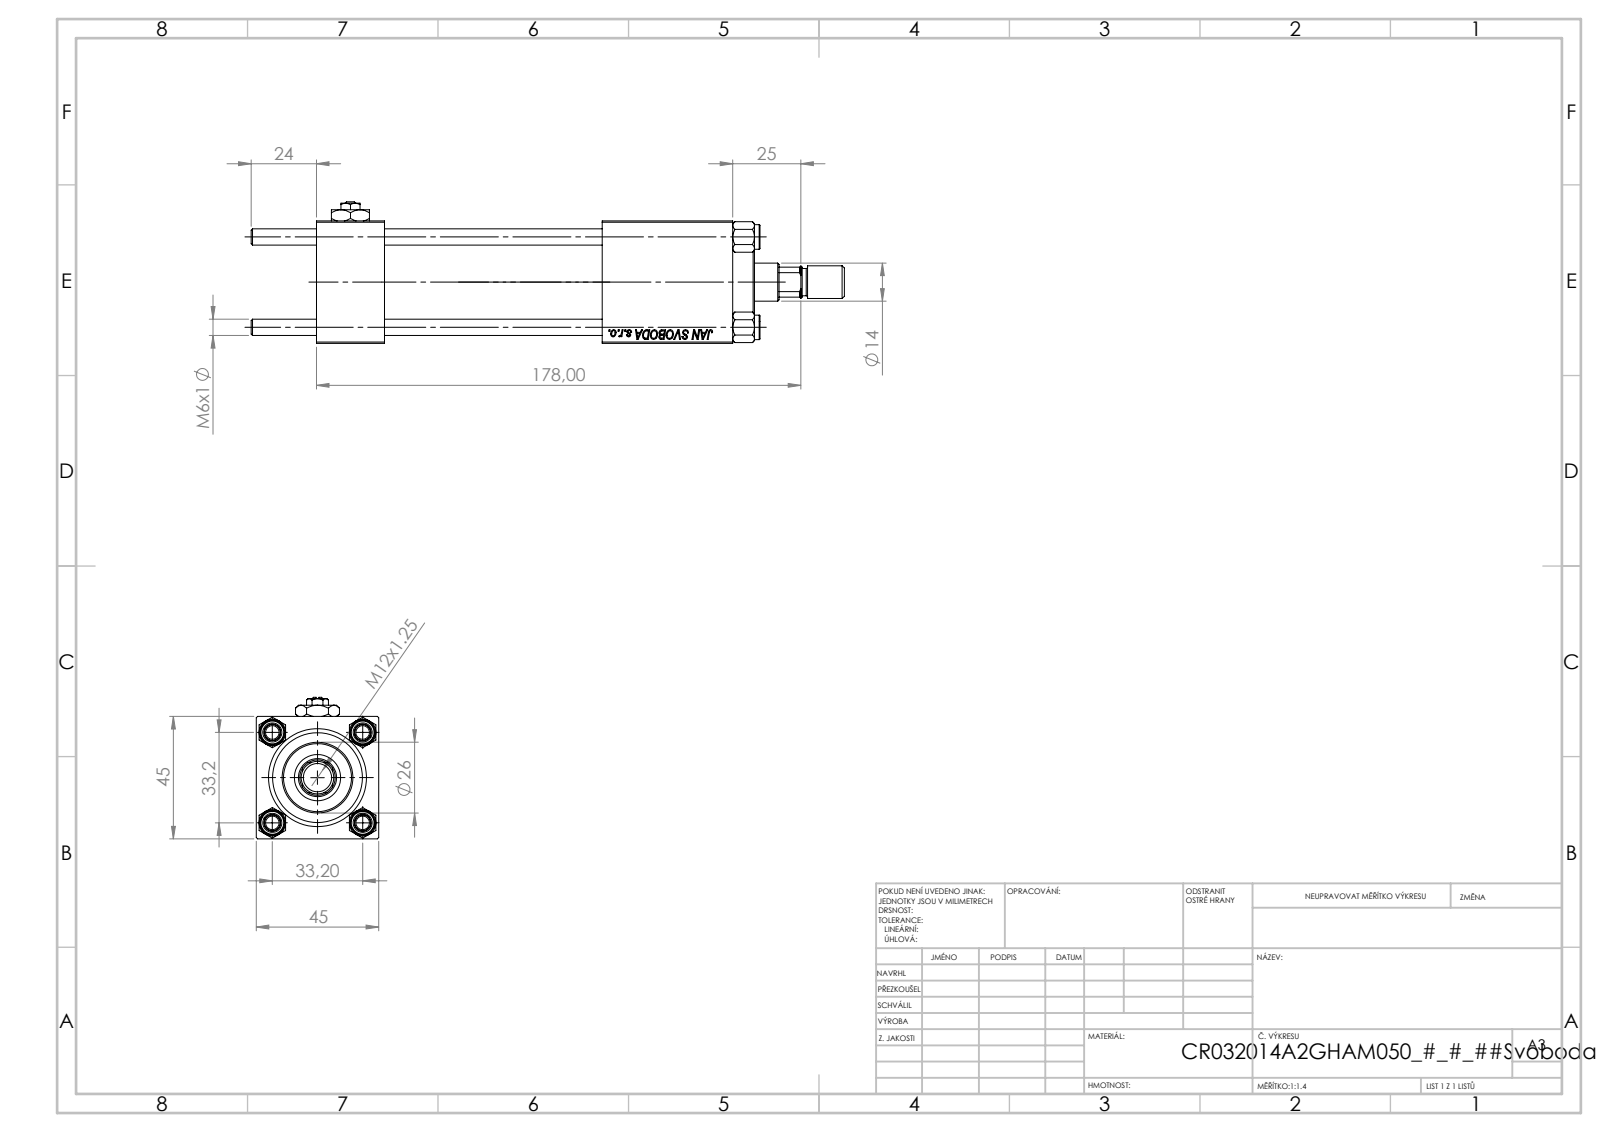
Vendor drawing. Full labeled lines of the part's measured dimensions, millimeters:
Part name (STEP PRODUCT): V215CR_BODY_A; Zatka_pro_OIL_PORT; V215CR_VCP; CR025_012_A_0_G_A_G_M_020_+#_##_TYCINKA (+3 more)
STEP written by: SolidWorks 2019 (CONFIG_CONTROL_DESIGN)
Units: millimetres
Bodies: 13 solids, 1198 faces (546 planar, 88 cylindrical, 564 other)
Overall size (bounding box): 218 × 52 × 45
Volume: 217 095 mm³ · Surface area: 84 931 mm²
Round holes (diameter × count): ⌀6 ×4, ⌀7 ×2, ⌀13.16 ×2, ⌀20 ×2, ⌀6.5 ×1, ⌀14 ×1, ⌀17 ×1, ⌀24 ×1, ⌀32 ×1, ⌀33 ×1
Round bosses / shafts (diameter × count): ⌀9 ×4, ⌀38 ×1, ⌀26 ×1, ⌀12 ×1, ⌀10 ×1
Partial cylindrical surfaces — rounded edges, fillets, slot ends (radius × count): R6.5 ×1
Main face-to-face distances: 45, 25, 153, 128, 105, 80, 48, 124.3, 99.3, 19.3
Hole centre spacings: 23.48, 33.2, 46.95, 105.5
